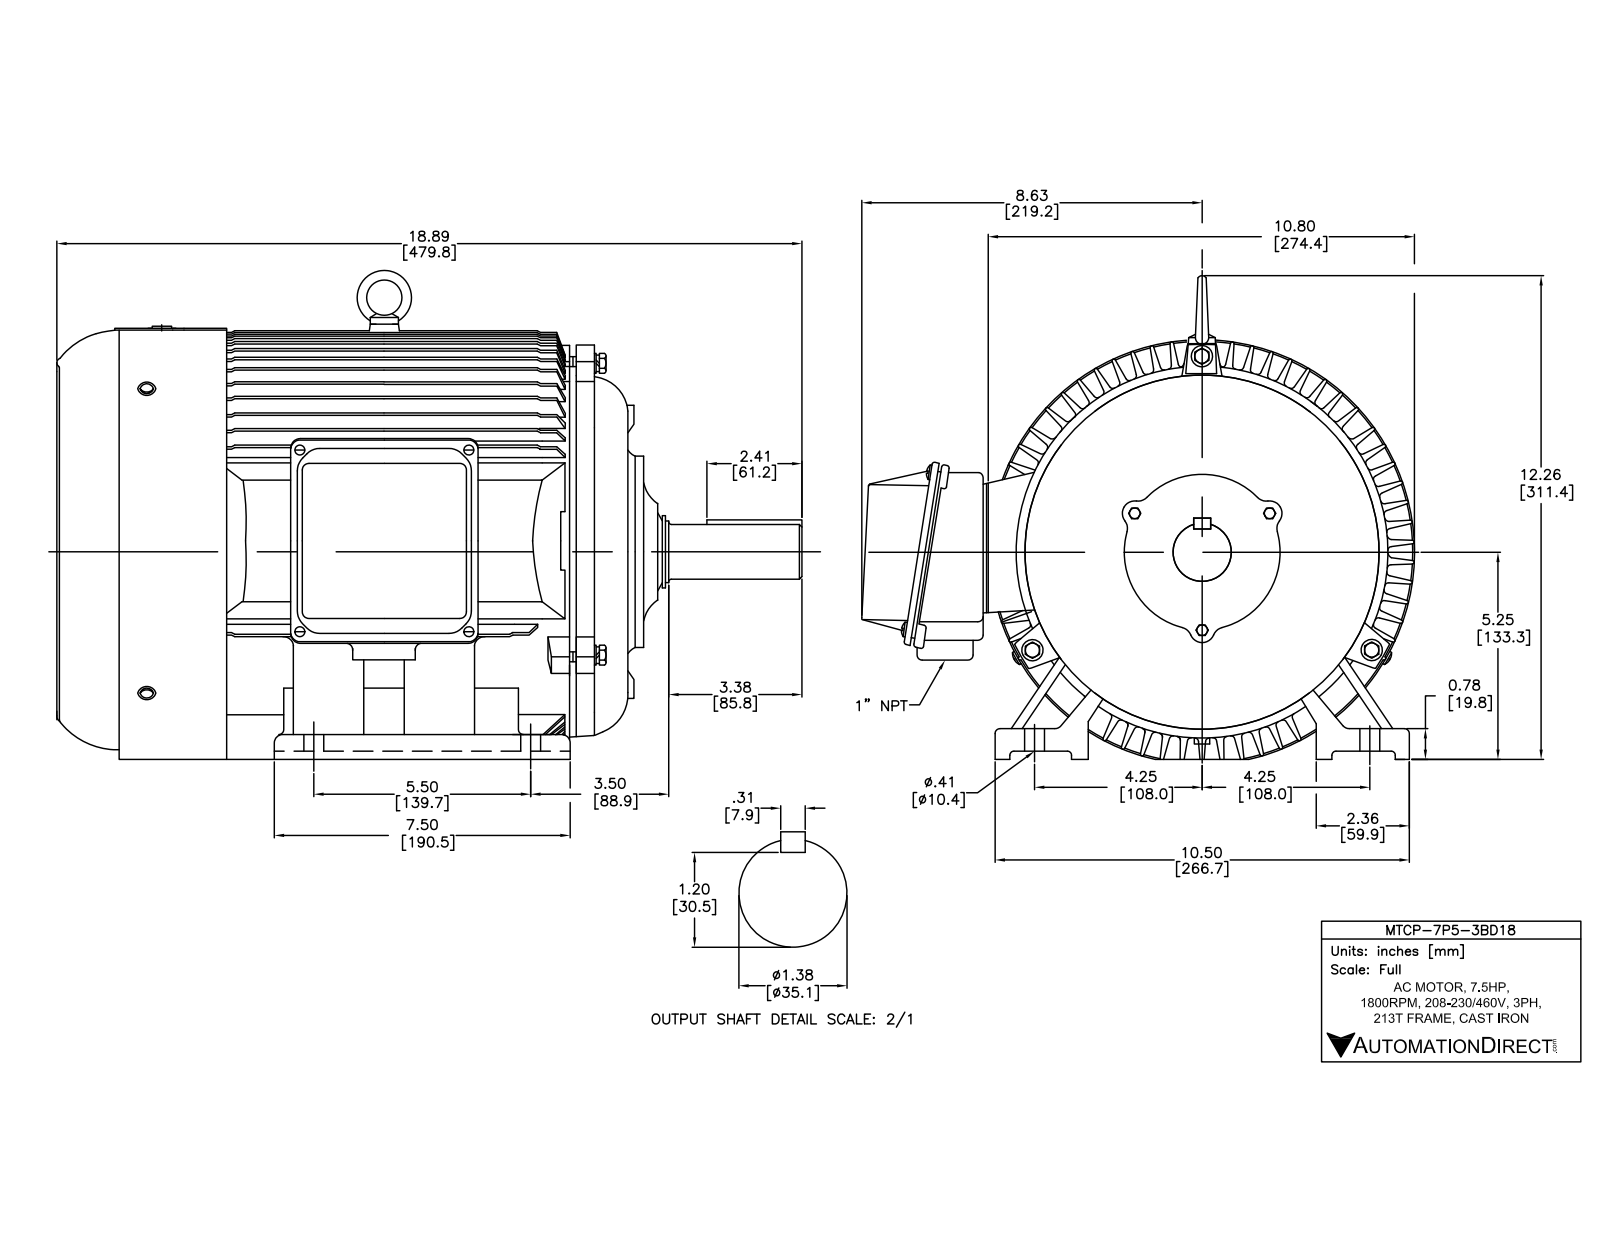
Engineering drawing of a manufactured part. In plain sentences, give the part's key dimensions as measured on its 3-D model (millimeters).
The part is named "hex head bolts-full thread grade c gb_GB_FASTENER_BOLT_HHBFTC M5X10-N; eyebolts gb_GB_FASTENER_SCREWS_FRS M10-N; PE210接线盒座_默认_按加工; spring lock washers--normal type gb_GB_FASTENER_WASHER_SW 5 (+6 more)". Its 3-D file was written by "SolidWorks 2017 (AUTOMOTIVE_DESIGN)". It is 48 solids with 2914 faces: 771 planar, 1085 cylindrical and 1058 other. Overall it measures 480.84 by 362.99 by 327.45 millimeters. Its volume is 3 890 000 cubic millimeters and its surface area 1 554 000 square millimeters. Round holes: 14 of diameter 5.8, 11 of diameter 4.2, 4 of diameter 10.5, 3 of diameter 5, 3 of diameter 5.3, 3 of diameter 5.4, 3 of diameter 6.8, 3 of diameter 8.4, 3 of diameter 8.68, 3 of diameter 10, 2 of diameter 2, 1 of diameter 8. Round bosses or shafts: 8 of diameter 5, 6 of diameter 8, 4 of diameter 10, 3 of diameter 16, 3 of diameter 12.88, 1 of diameter 288.4, 1 of diameter 254, 1 of diameter 245. Partial cylindrical surfaces (rounded edges, fillets, slot ends): 272 of radius 1, 67 of radius 0.5, 66 of radius 3, 39 of radius 1.25, 28 of radius 7, 16 of radius 2, 11 of radius 8, 10 of radius 2.5. The main face-to-face distances are 5, 1.2, 306, 6, 3, 74.64, 75.84, 381.84, 380.64, 81.84. The hole center spacings are 68, 96.17, 68.01, 100, 132, 68.02, 96.18, 109.93.
